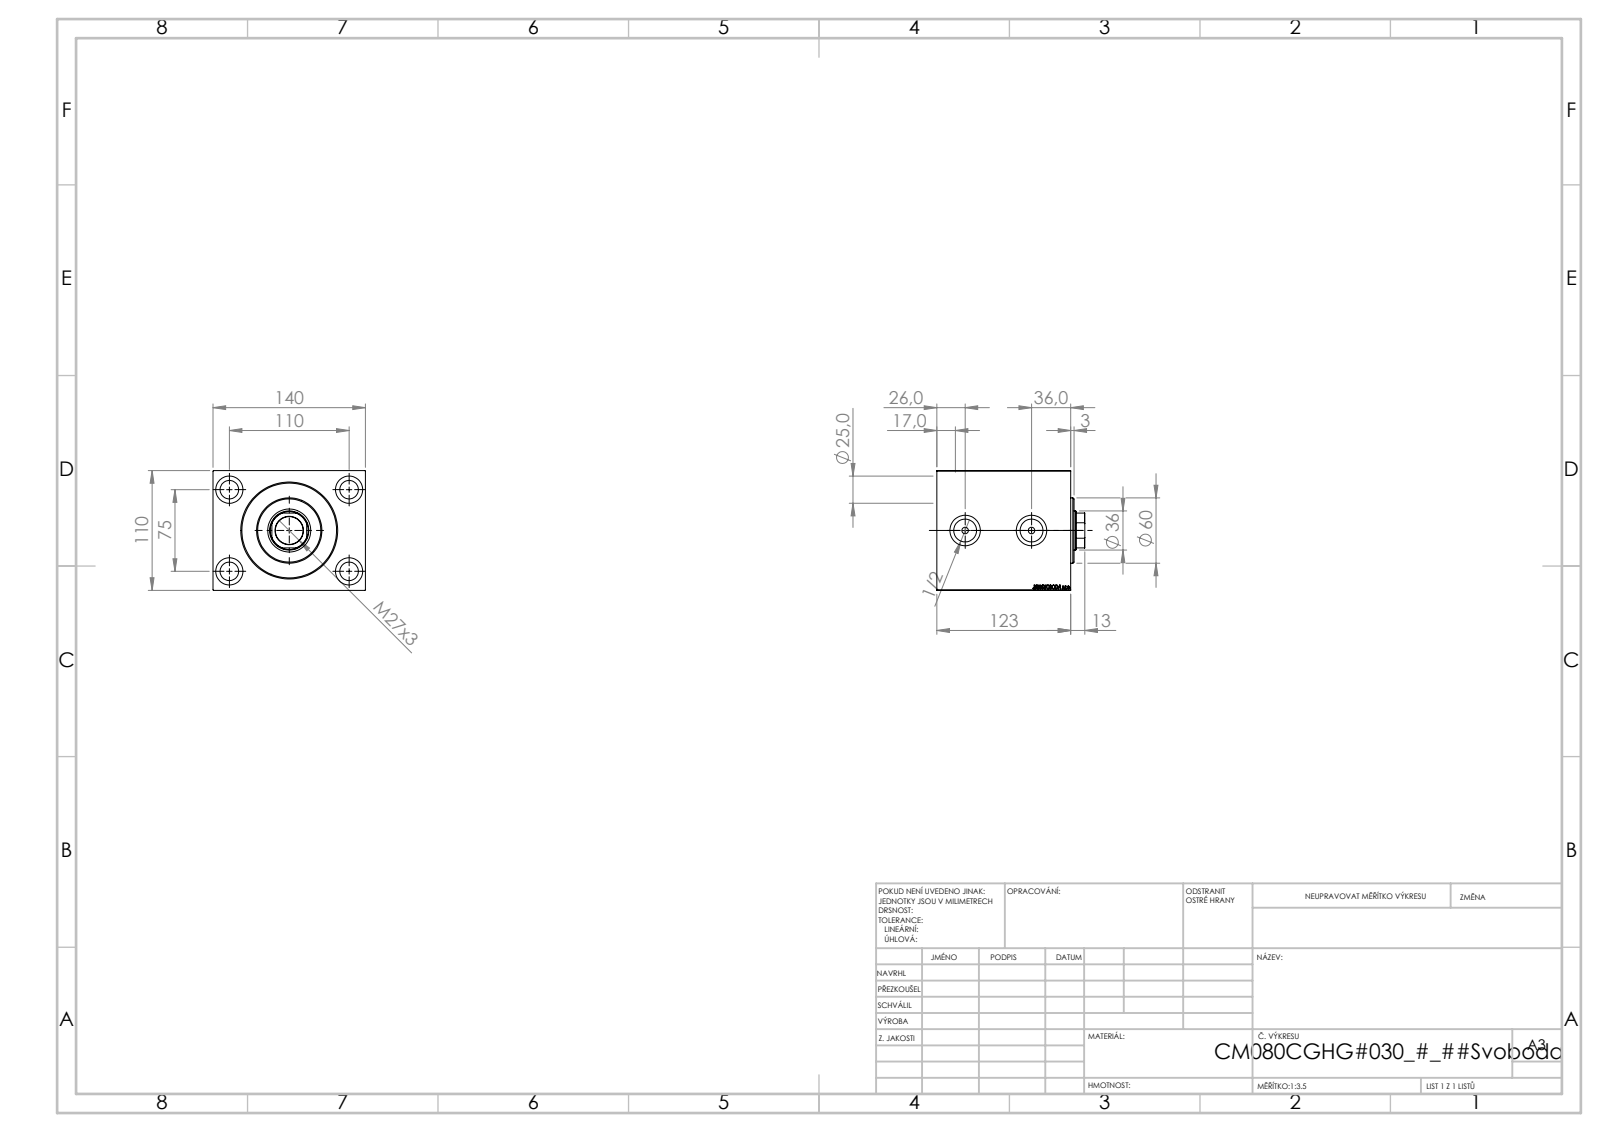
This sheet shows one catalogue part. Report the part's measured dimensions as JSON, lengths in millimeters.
{"part_name": "V450CM_VC_B; V450CM_C_VCP; V450CM_C_Body", "step_written_by": "SolidWorks 2019 (CONFIG_CONTROL_DESIGN)", "units": "millimeters", "bodies": {"solids": 3, "faces": 866, "planar": 410, "cylindrical": 62, "other": 394}, "overall_size": [140, 136, 110], "volume_mm3": 1695000, "surface_area_mm2": 177388, "round_holes": [[17, 4], [25, 4], [6, 2], [20.96, 2], [28, 2], [25.5, 1], [36, 1], [39.5, 1], [80, 1], [82, 1], [87, 1]], "round_bosses_or_shafts": [[60, 1]], "partial_cylinders_radius": [[17.5, 1]], "face_to_face_distances": [110, 140, 123, 51, 72, 21.6, 29.4, 101.4, 10, 31.6], "hole_center_spacings": [66.57, 75, 110, 133.14, 61]}
